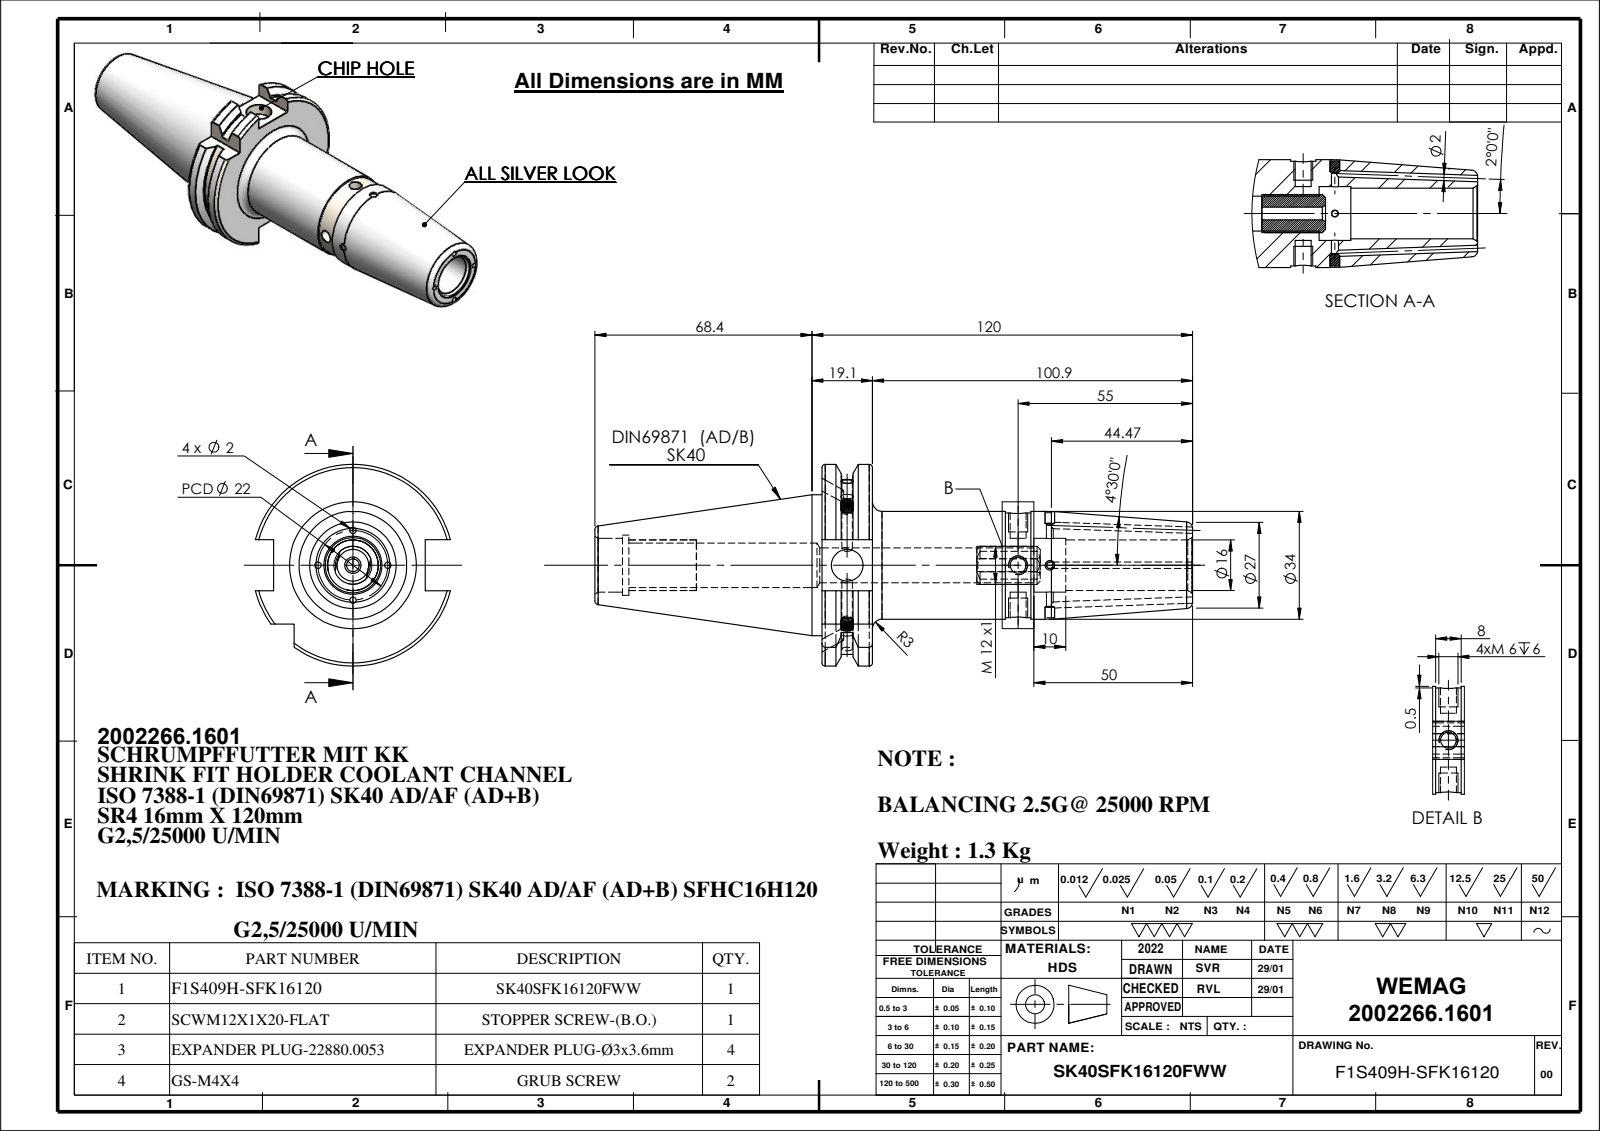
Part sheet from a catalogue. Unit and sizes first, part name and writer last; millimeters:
Units: millimetres
Overall size (bounding box): 188.4 × 63.55 × 61.48
Round holes (diameter × count): ⌀2 ×4, ⌀2.2 ×2, ⌀3 ×2, ⌀5 ×2, ⌀3.3 ×1, ⌀4 ×1, ⌀10 ×1, ⌀11 ×1, ⌀14 ×1, ⌀15.99 ×1, ⌀16.99 ×1, ⌀17 ×1
Round bosses / shafts (diameter × count): ⌀4 ×2, ⌀44.45 ×1, ⌀34 ×1, ⌀33 ×1
Partial cylindrical surfaces — rounded edges, fillets, slot ends (radius × count): R6 ×1, R28.12 ×1, R31.77 ×1
Main face-to-face distances: 15.9, 10, 16.1, 47.8, 60.9, 76.8, 116.8, 100.9, 71.6, 87.5
Hole centre spacings: 10, 53.85, 63.85
Volume: 168 330 mm³ · Surface area: 38 720 mm²
Bodies: 8 solids, 287 faces (66 planar, 103 cylindrical, 118 other)
Part name (STEP PRODUCT): SK40SFK16120FWW; 91406-SR416120; SCWM12X1X20-FLAT; EXPANDER PLUG Ø3x3.6 (+1 more)
STEP written by: SolidWorks 2018 (AUTOMOTIVE_DESIGN)
